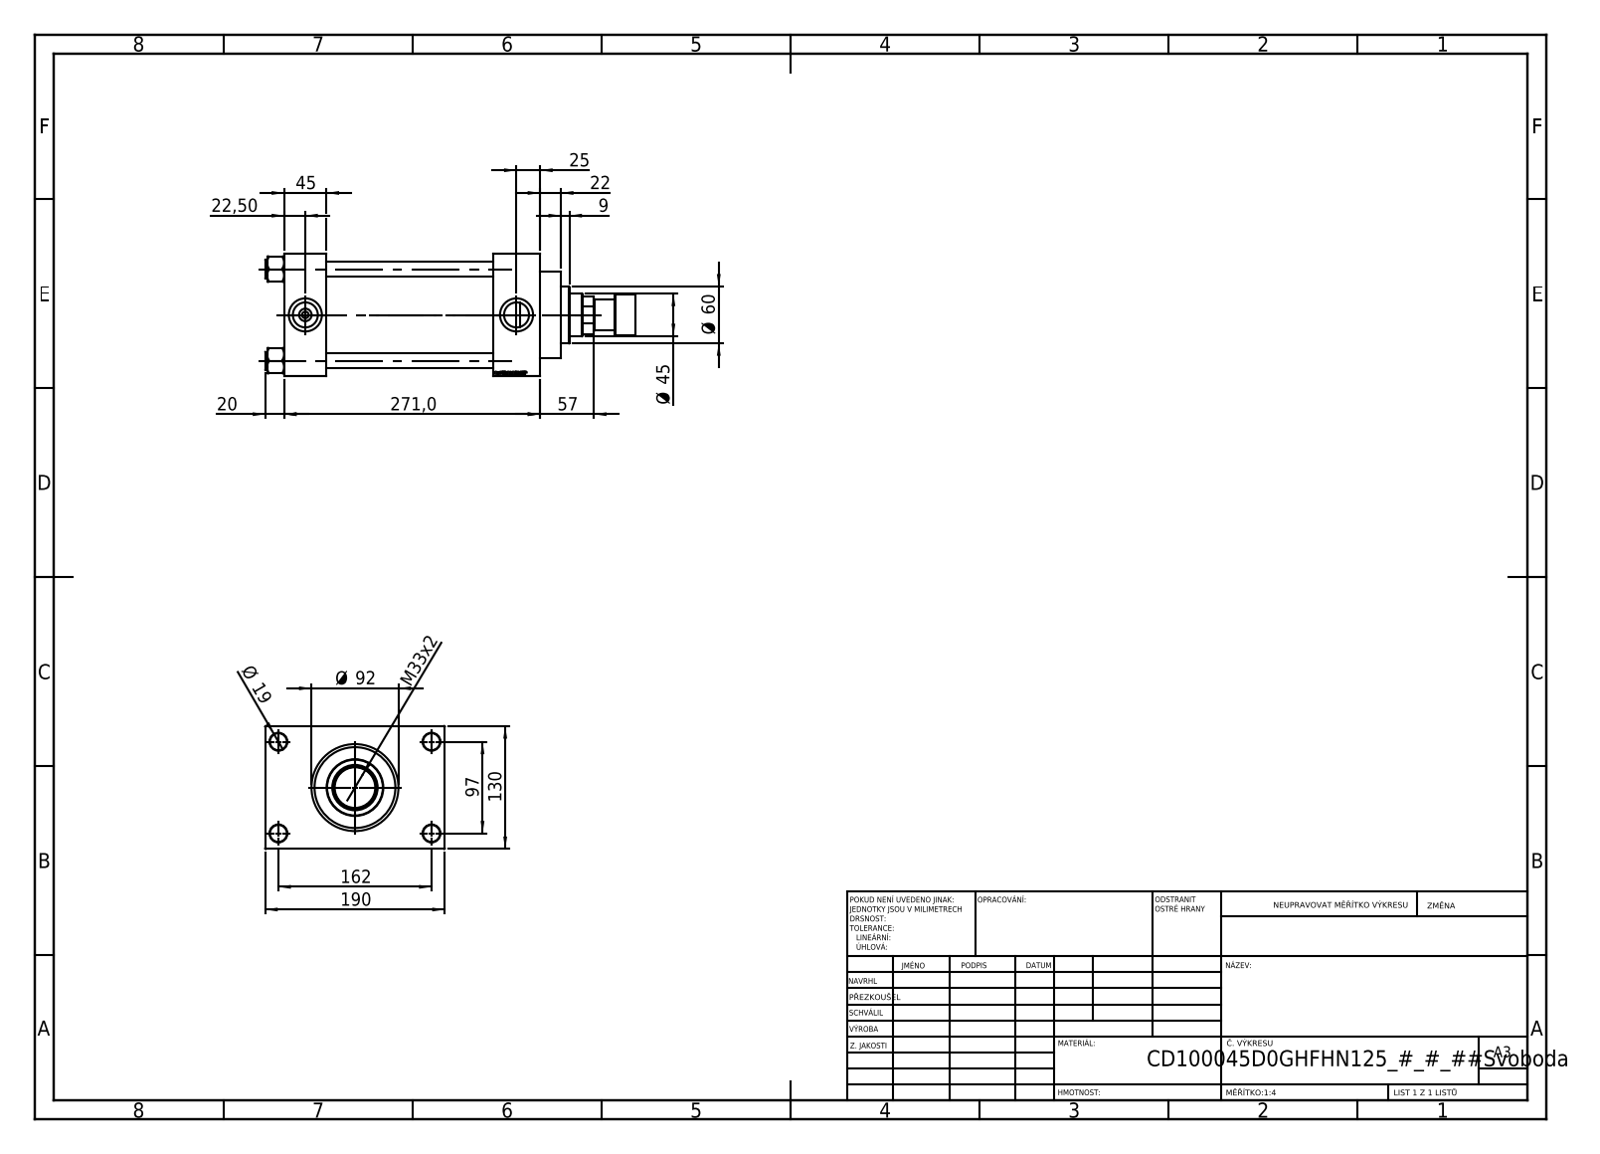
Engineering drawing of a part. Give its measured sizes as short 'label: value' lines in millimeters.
name: V215CD_D_TYCINKA; V215CD_D_Body; V215CR_ROD_END_F; V215CD_NUT_M5_D (+2 more)
written by: SolidWorks 2019 (CONFIG_CONTROL_DESIGN)
unit: mm
bodies: 12 solids, 1164 faces (548 planar, 92 cylindrical, 524 other)
size: 392 × 190 × 130
volume: 2 996 000 mm³; area: 467 164 mm²
holes: 4× ⌀16, 4× ⌀18, 2× ⌀7, 2× ⌀26.44, 2× ⌀35, 1× ⌀31.5, 1× ⌀45, 1× ⌀48, 1× ⌀76, 1× ⌀85.5, 1× ⌀100
bosses: 4× ⌀19, 1× ⌀106, 1× ⌀92, 1× ⌀60, 1× ⌀44, 1× ⌀33
face distances: 130, 45, 221, 176, 271, 226, 50, 30, 160, 125
hole spacings: 32.55, 68.52, 94.41, 96.9, 102.27, 129.45, 161.73, 97
